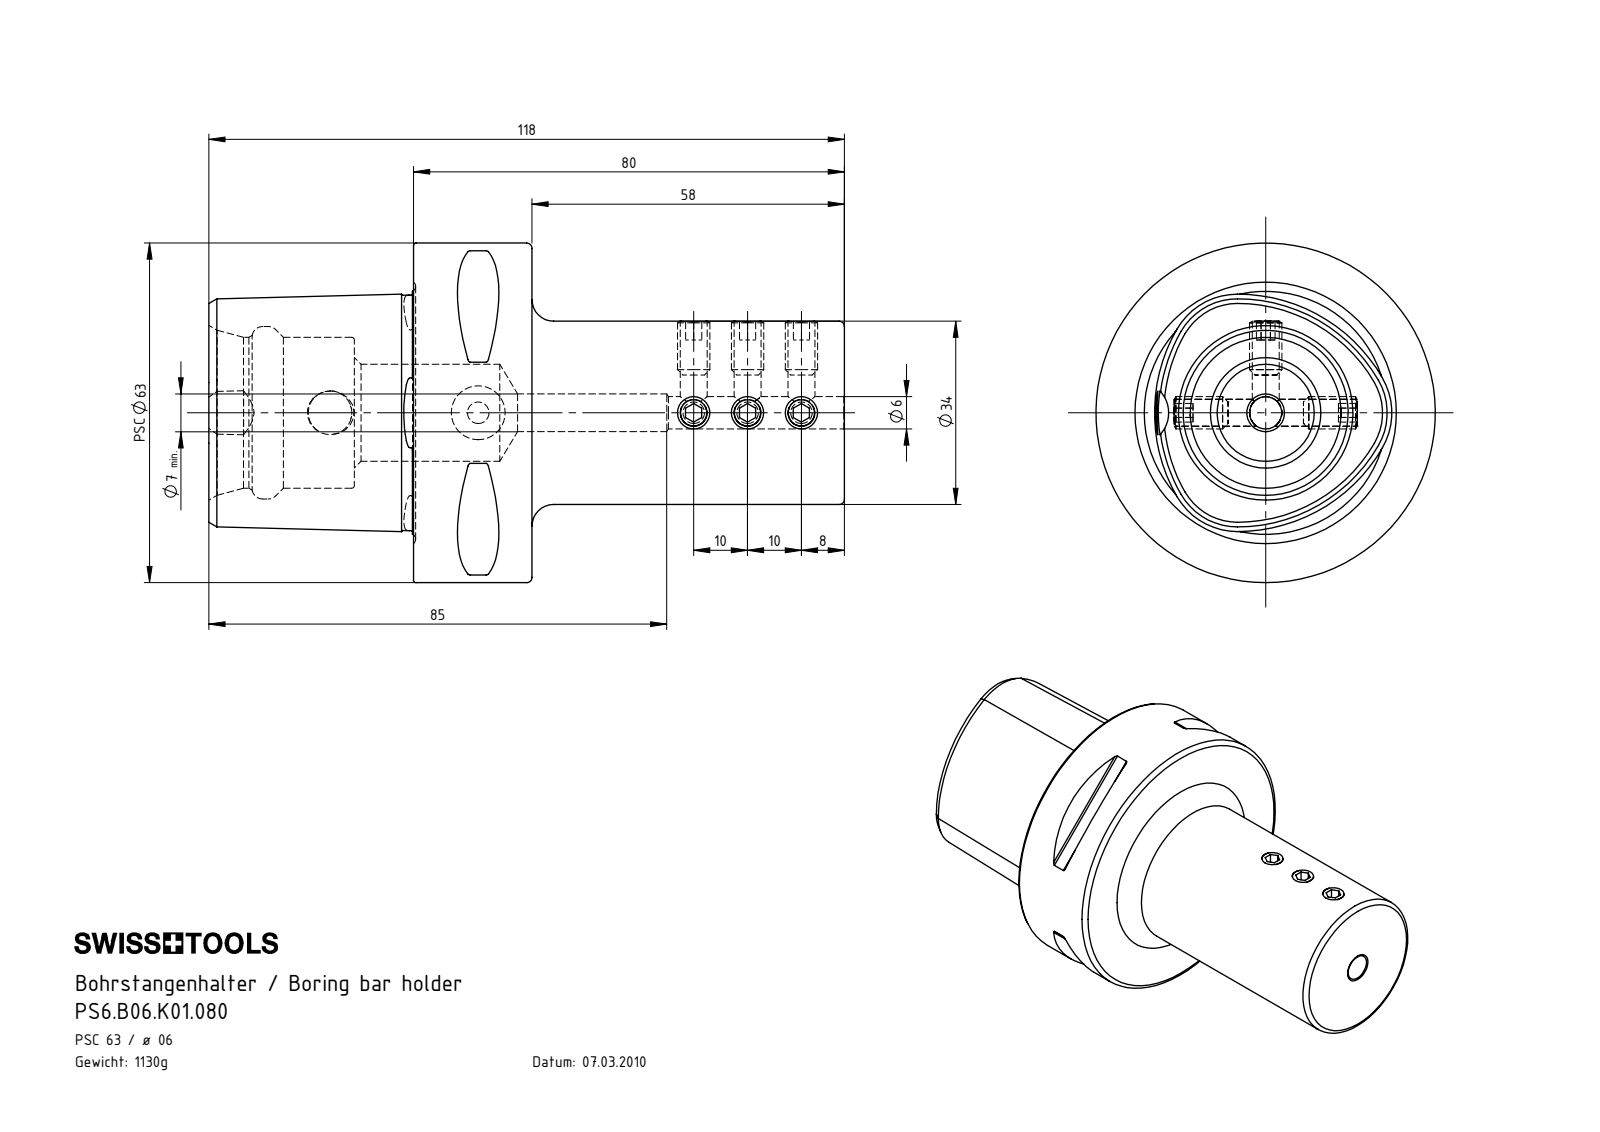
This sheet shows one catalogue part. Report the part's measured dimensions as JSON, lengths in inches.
{"part_name": "ISO 4026 - M6 x 10_PreviewCfg; PS6.B06.K01.080; PS6-B06.K01.080_A", "step_written_by": "SolidWorks 2017 (AUTOMOTIVE_DESIGN)", "units": "inches", "bodies": {"solids": 10, "faces": 288, "planar": 101, "cylindrical": 70, "other": 117}, "overall_size": [4.646, 2.48, 2.48], "volume_in3": 8.927, "surface_area_in2": 48.22, "round_holes": [[0.197, 6], [0.157, 1], [0.236, 1], [0.276, 1], [0.319, 1], [0.709, 1], [1.102, 1], [1.26, 1]], "round_bosses_or_shafts": [[0.236, 6], [2.48, 1], [1.339, 1]], "partial_cylinders_radius": [[0.02, 8], [0.236, 1]], "face_to_face_distances": [0.866, 3.15, 2.283, 1.496, 2.362, 4.646, 0.98, 1.063, 0.394, 0.433], "hole_center_spacings": [0.394, 0.787, 1.083, 1.575, 1.969, 2.362, 2.657, 3.051]}
